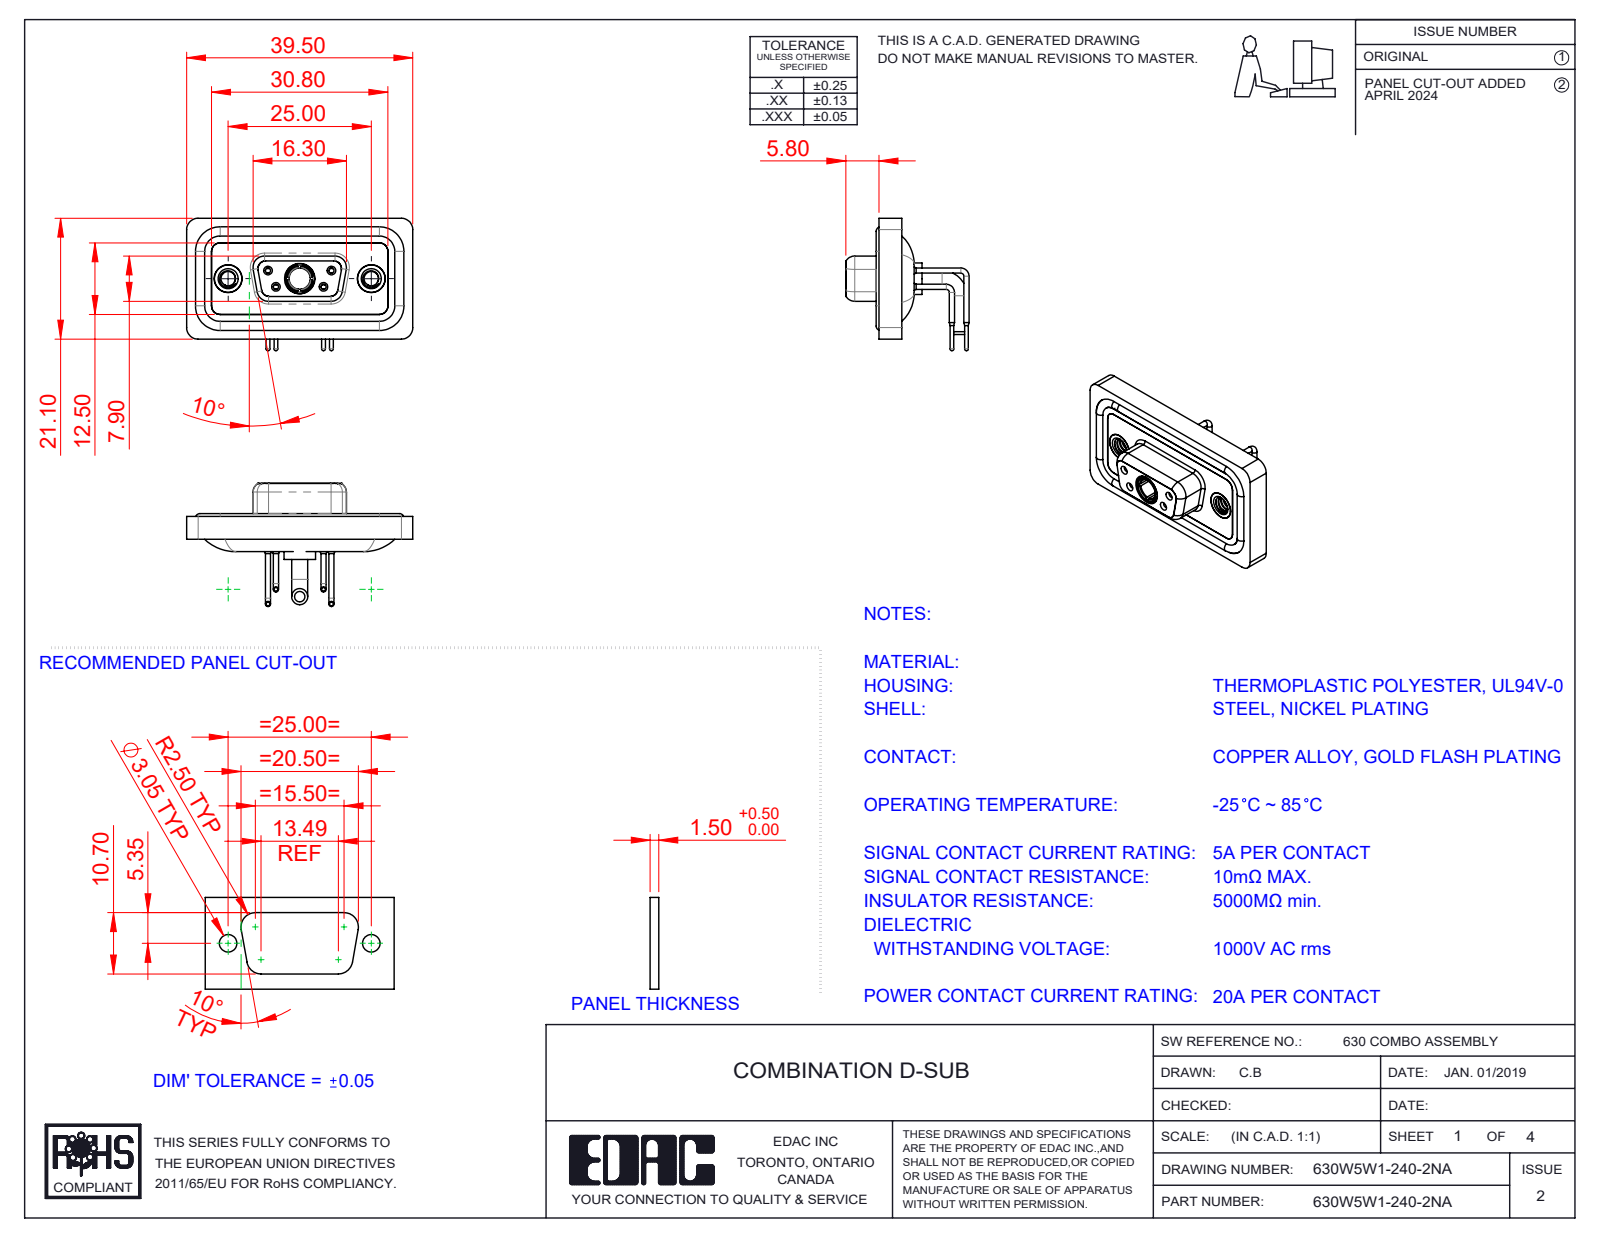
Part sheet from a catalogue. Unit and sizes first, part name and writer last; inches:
Units: inches
Overall size (bounding box): 1.555 × 0.91 × 0.848
Round holes (diameter × count): ⌀0.035 ×4, ⌀0.043 ×4, ⌀0.059 ×4, ⌀0.079 ×4, ⌀0.191 ×3, ⌀0.063 ×2, ⌀0.067 ×2, ⌀0.098 ×2, ⌀0.157 ×2, ⌀0.159 ×2, ⌀0.197 ×2, ⌀0.146 ×1
Round bosses / shafts (diameter × count): ⌀0.063 ×6, ⌀0.035 ×4, ⌀0.026 ×4, ⌀0.195 ×2, ⌀0.189 ×2, ⌀0.11 ×2, ⌀0.217 ×1, ⌀0.205 ×1
Partial cylindrical surfaces — rounded edges, fillets, slot ends (radius × count): R0.059 ×18, R0.079 ×18, R0.053 ×8, R0.063 ×8, R0.01 ×4, R0.02 ×4, R0.024 ×4, R0.026 ×4
Main face-to-face distances: 0.016, 0.071, 0.043, 0.114, 0.098, 0.063, 0.122, 0.083, 0.059, 0.02
Hole centre spacings: 0.124, 0.225, 0.28, 0.492, 0.713, 0.173, 0.173, 0.327
Volume: 0.294 in³ · Surface area: 12.16 in²
Bodies: 13 solids, 670 faces (194 planar, 303 cylindrical, 173 other)
Part name (STEP PRODUCT): 630Combo Contact Row 1_50 Contacts; 630Combo Housing_5W1; 630W5W1-140-2NA; 630Combo Threaded Rivet_A (+5 more)
STEP written by: SolidWorks 2023 (CONFIG_CONTROL_DESIGN)
